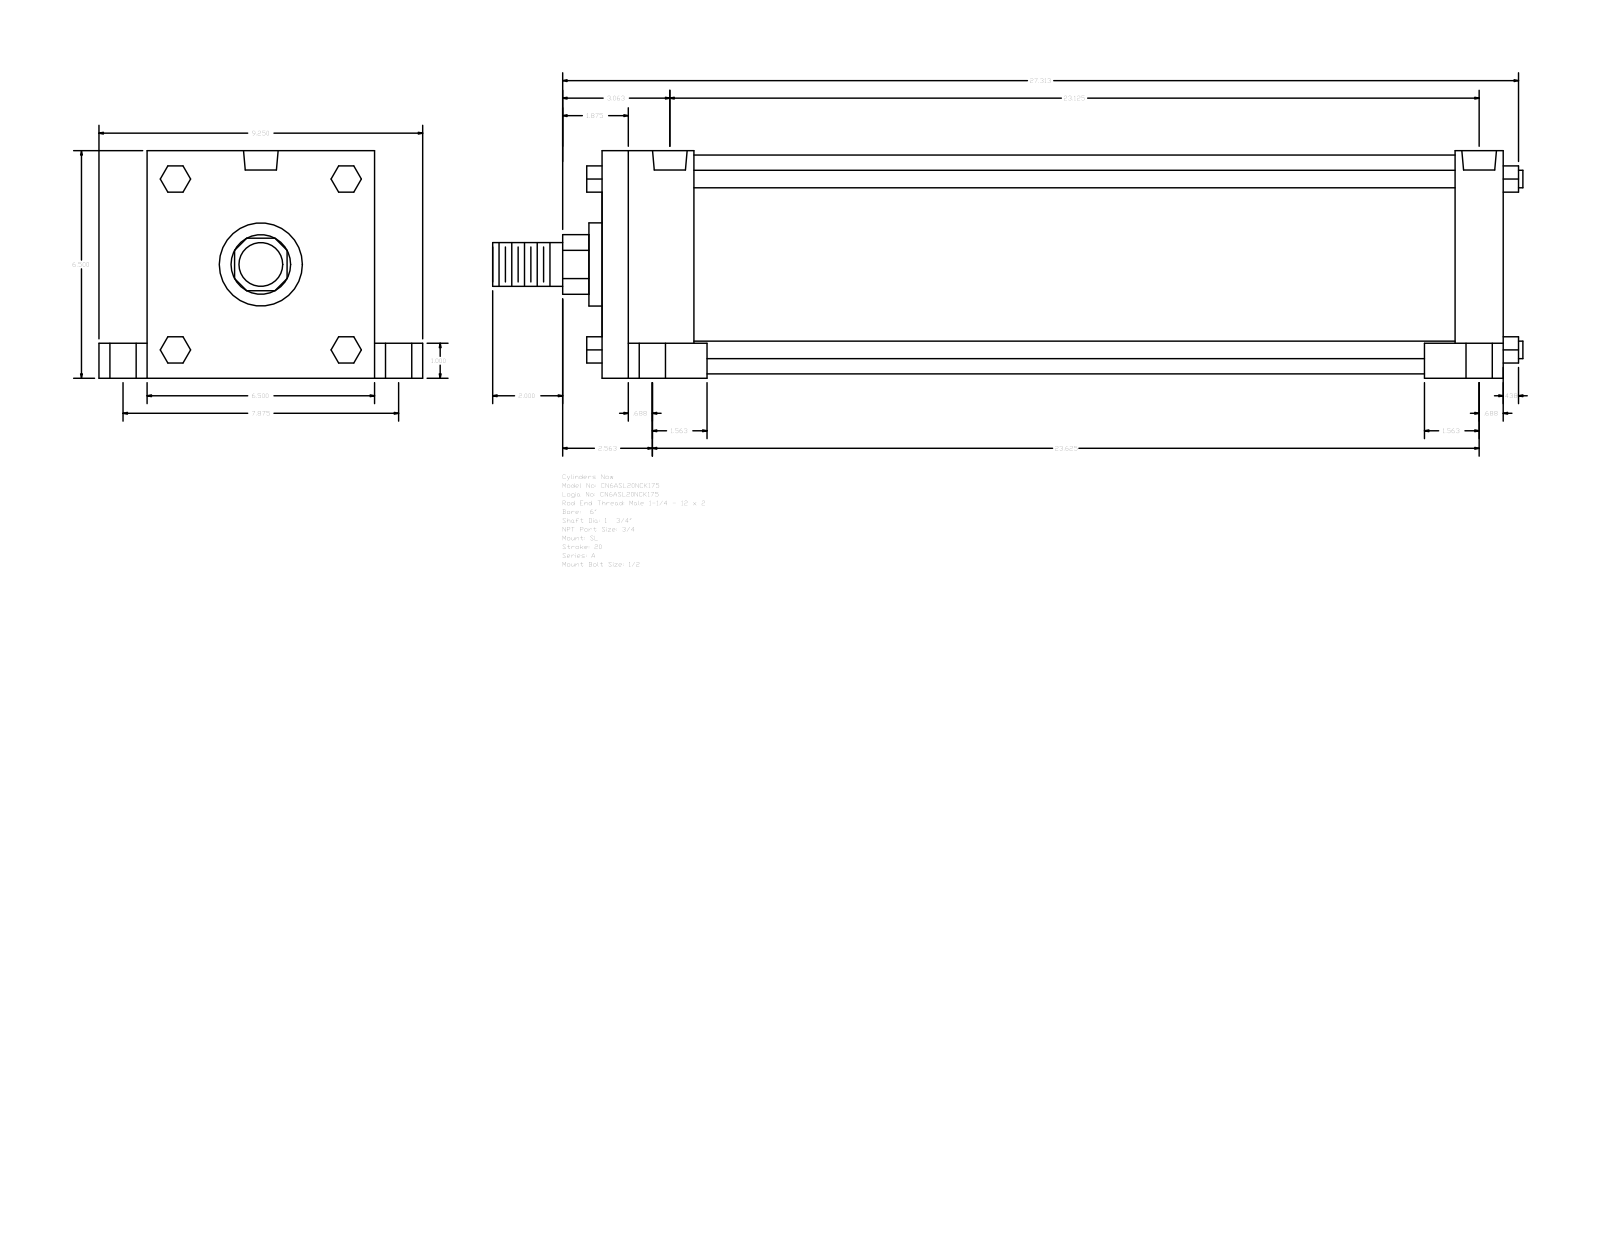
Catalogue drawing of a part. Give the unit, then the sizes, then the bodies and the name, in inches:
Units: inches
Overall size (bounding box): 29.437 × 9.25 × 6.5
Round holes (diameter × count): ⌀0.594 ×4, ⌀0.75 ×4, ⌀1 ×4, ⌀0.989 ×2
Round bosses / shafts (diameter × count): ⌀0.5 ×4, ⌀6.25 ×1, ⌀2.375 ×1, ⌀1.75 ×1, ⌀1.25 ×1
Partial cylindrical surfaces — rounded edges, fillets, slot ends (radius × count): R0.852 ×1
Main face-to-face distances: 6.5, 25.75, 1.375, 2.625, 23.125, 24.375, 21.75, 1, 5.5, 7.875
Hole centre spacings: 0.219, 3.937, 3.943, 3.969, 4.002, 7.875, 22.687, 22.906
Bodies: 0 solids, 150 faces (114 planar, 36 cylindrical, 0 other)
Part name (STEP PRODUCT): A_SL__0600_1.75
STEP written by: GSSL Pune (CONFIG_CONTROL_DESIGN)
